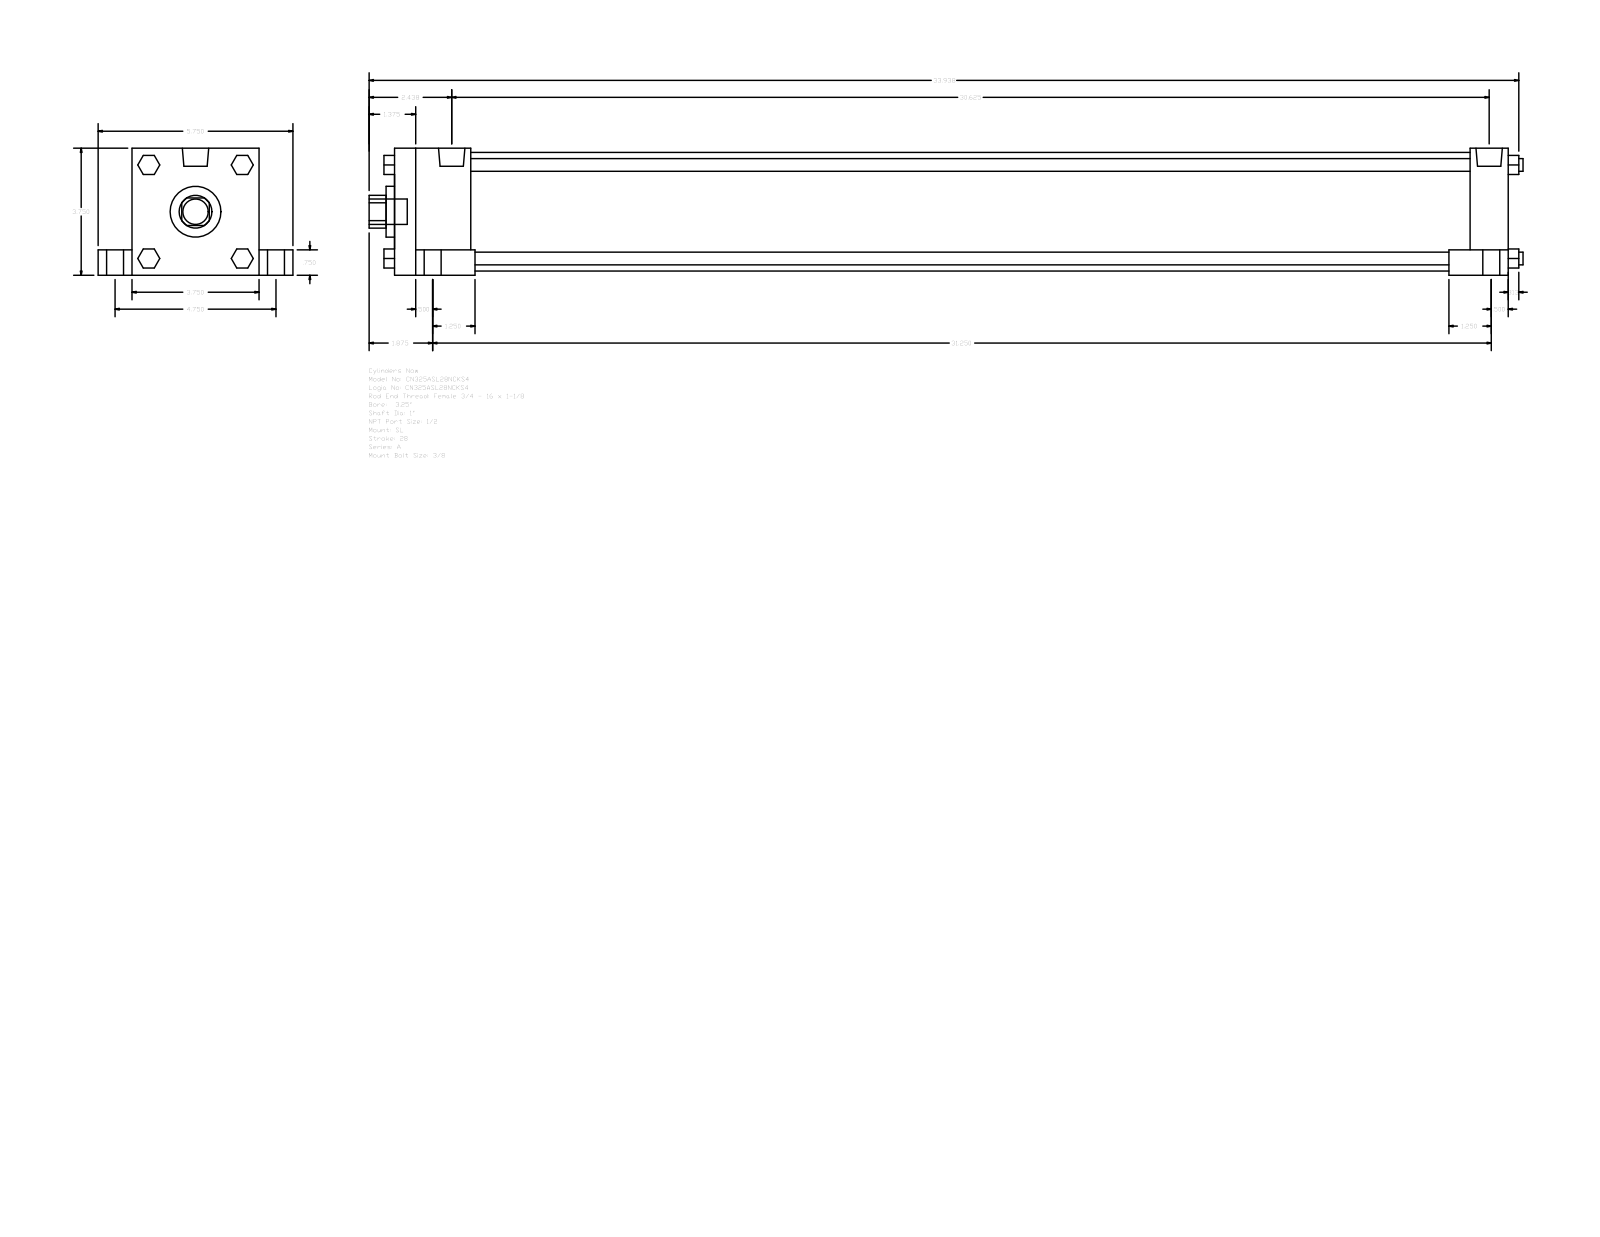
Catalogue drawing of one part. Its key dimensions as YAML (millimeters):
part_name: "A_SL__0325_1"
step_written_by: "GSSL Pune (CONFIG_CONTROL_DESIGN)"
units: millimeters
bodies: {solids: 0, faces: 150, planar: 114, cylindrical: 36, other: 0}
overall_size: [865.19, 146.05, 95.25]
round_holes:
  - {diameter: 25.4, count: 1}
  - {diameter: 38.1, count: 1}
  - {diameter: 88.9, count: 1}
round_bosses_or_shafts:
  - {diameter: 19.05, count: 5}
  - {diameter: 12.7, count: 4}
  - {diameter: 9.53, count: 4}
  - {diameter: 8.73, count: 4}
  - {diameter: 19.77, count: 2}
partial_cylinders:
  - {radius: 12.29, count: 1}
face_to_face_distances: [95.24, 835.03, 19.05, 25.41, 120.65, 76.19, 57.15, 806.45, 749.3, 777.88]
